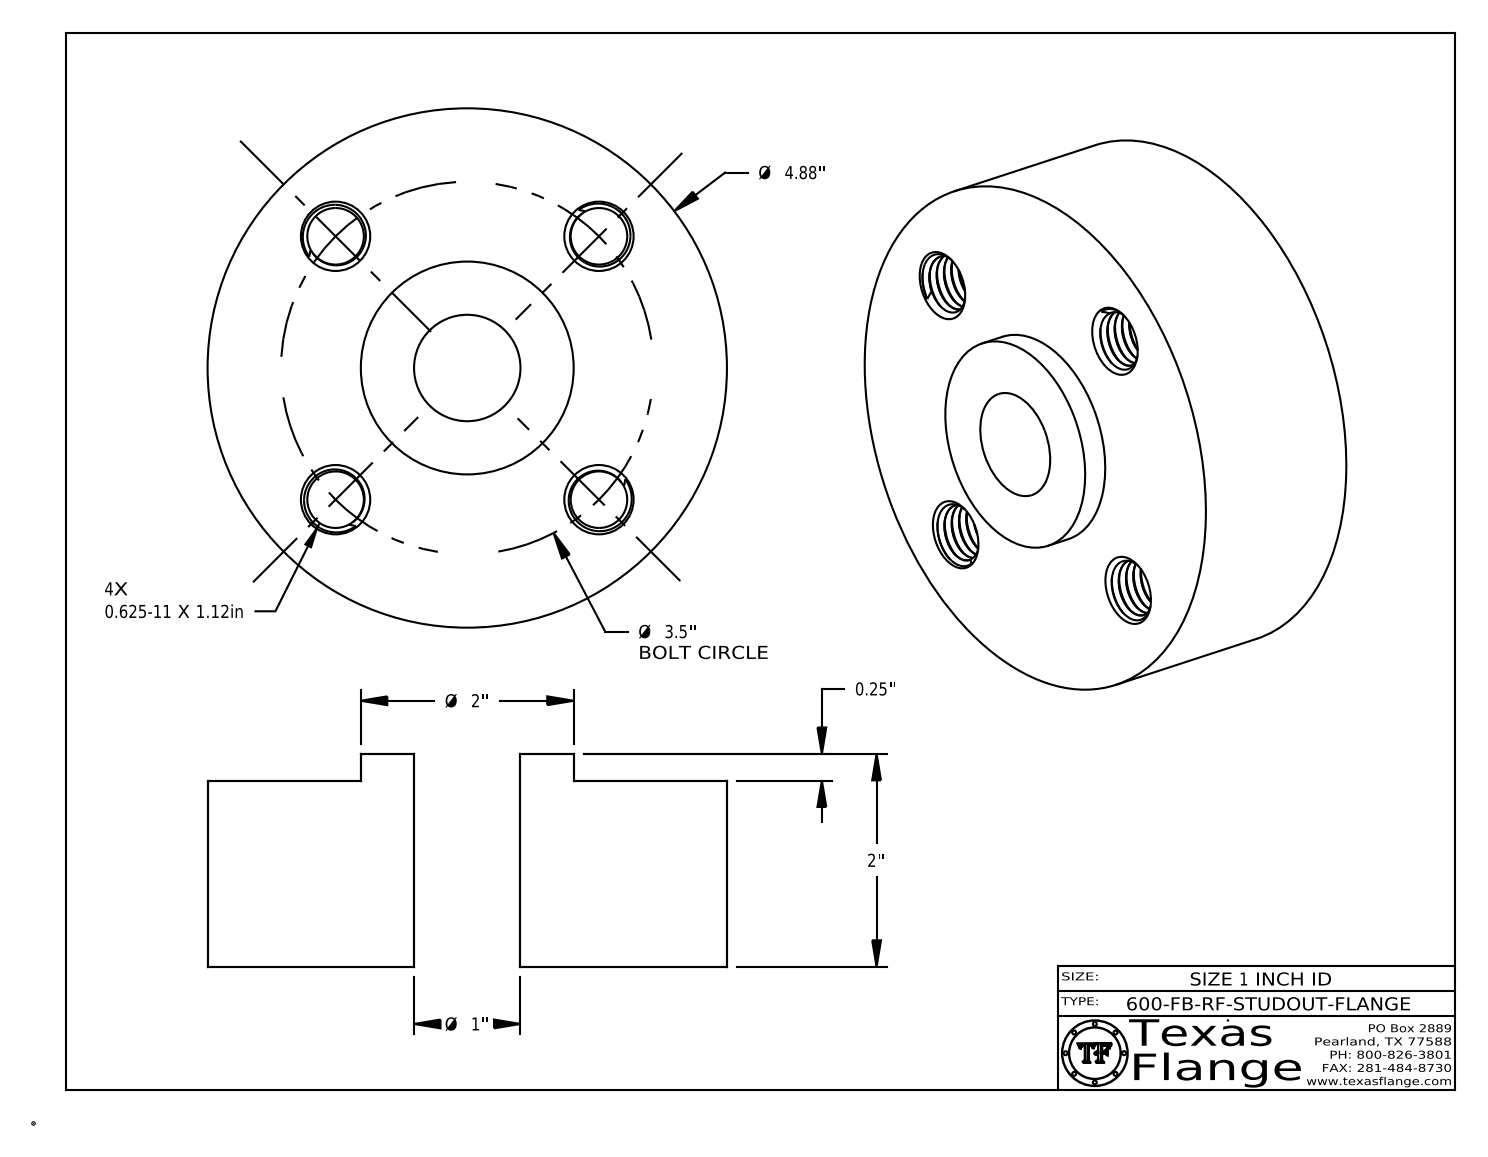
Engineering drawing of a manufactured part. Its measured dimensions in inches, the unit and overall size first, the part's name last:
Units: inches
Overall size (bounding box): 4.88 × 4.88 × 2
Round holes (diameter × count): ⌀0.531 ×4, ⌀1 ×2
Round bosses / shafts (diameter × count): ⌀0.061 ×8, ⌀4.88 ×1, ⌀2 ×1, ⌀0.788 ×1
Main face-to-face distances: 1.75, 0.25, 2, 1.985, 1.735, 0.015, 0.298, 0.293, 0.054, 0.248
Hole centre spacings: 1.75, 2.475, 1.339, 3.233, 3.5
Volume: 30.78 in³ · Surface area: 80.6 in²
Bodies: 1 solid, 618 faces (368 planar, 98 cylindrical, 152 other)
Part name (STEP PRODUCT): 1-600-FB-RF-STUDOUT-FLANGE
STEP written by: CATIA V5 STEP AP214 (AUTOMOTIVE_DESIGN)
